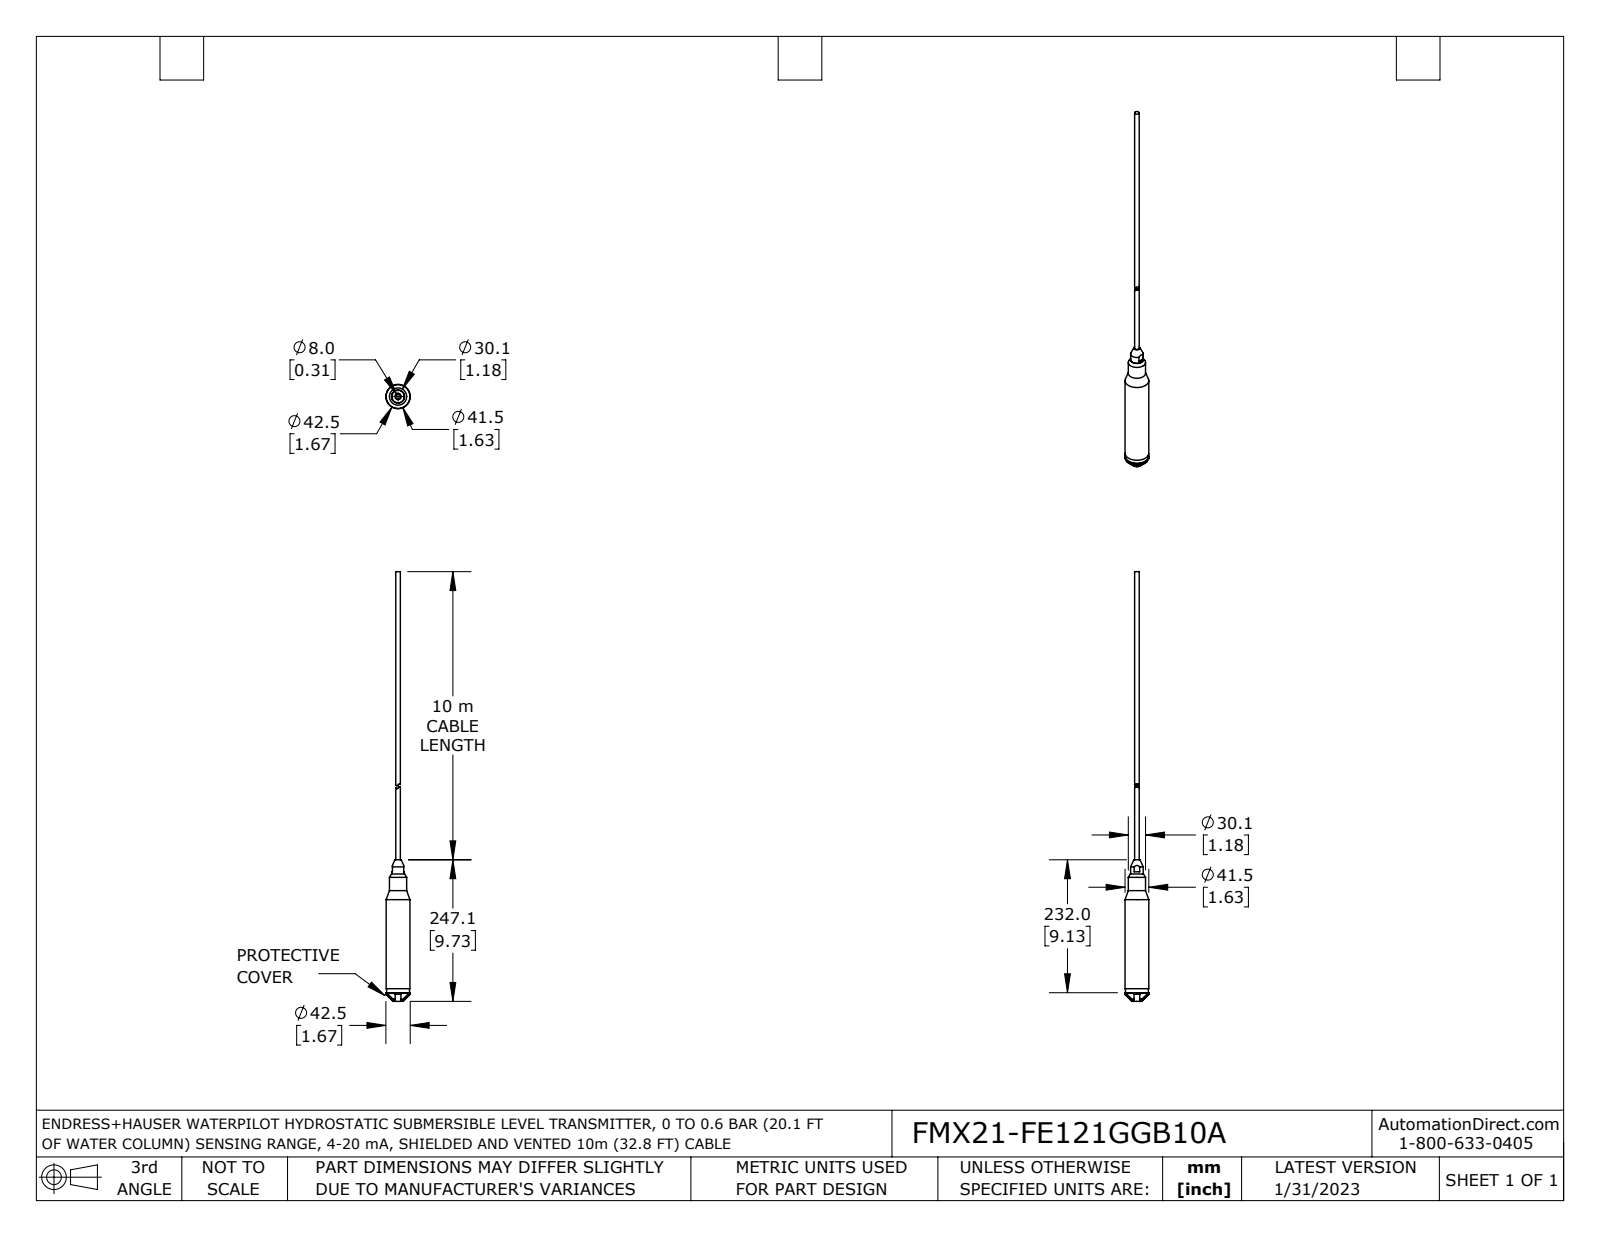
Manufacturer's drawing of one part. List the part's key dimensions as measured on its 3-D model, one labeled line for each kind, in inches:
Part name (STEP PRODUCT): 3D_FMX21-30WQ2_0_NoTag_4546161 250mm CUT 1 coord fxt
STEP written by: SolidWorks 2021 (AUTOMOTIVE_DESIGN)
Units: inches
Bodies: 2 solids, 66 faces (24 planar, 32 cylindrical, 10 other)
Overall size (bounding box): 29.528 × 1.673 × 1.673
Volume: 17.65 in³ · Surface area: 68.68 in²
Round holes (diameter × count): ⌀1.575 ×1
Round bosses / shafts (diameter × count): ⌀1.673 ×1, ⌀1.634 ×1, ⌀1.577 ×1, ⌀1.185 ×1, ⌀0.864 ×1, ⌀0.315 ×1
Partial cylindrical surfaces — rounded edges, fillets, slot ends (radius × count): R0.178 ×4, R0.061 ×2, R0.067 ×2, R0.092 ×2, R0.128 ×2, R0.148 ×2
Main face-to-face distances: 0.594, 0.077, 0.517, 0.192, 0.586, 0.394, 0.553, 0.476, 0.042, 0.778
